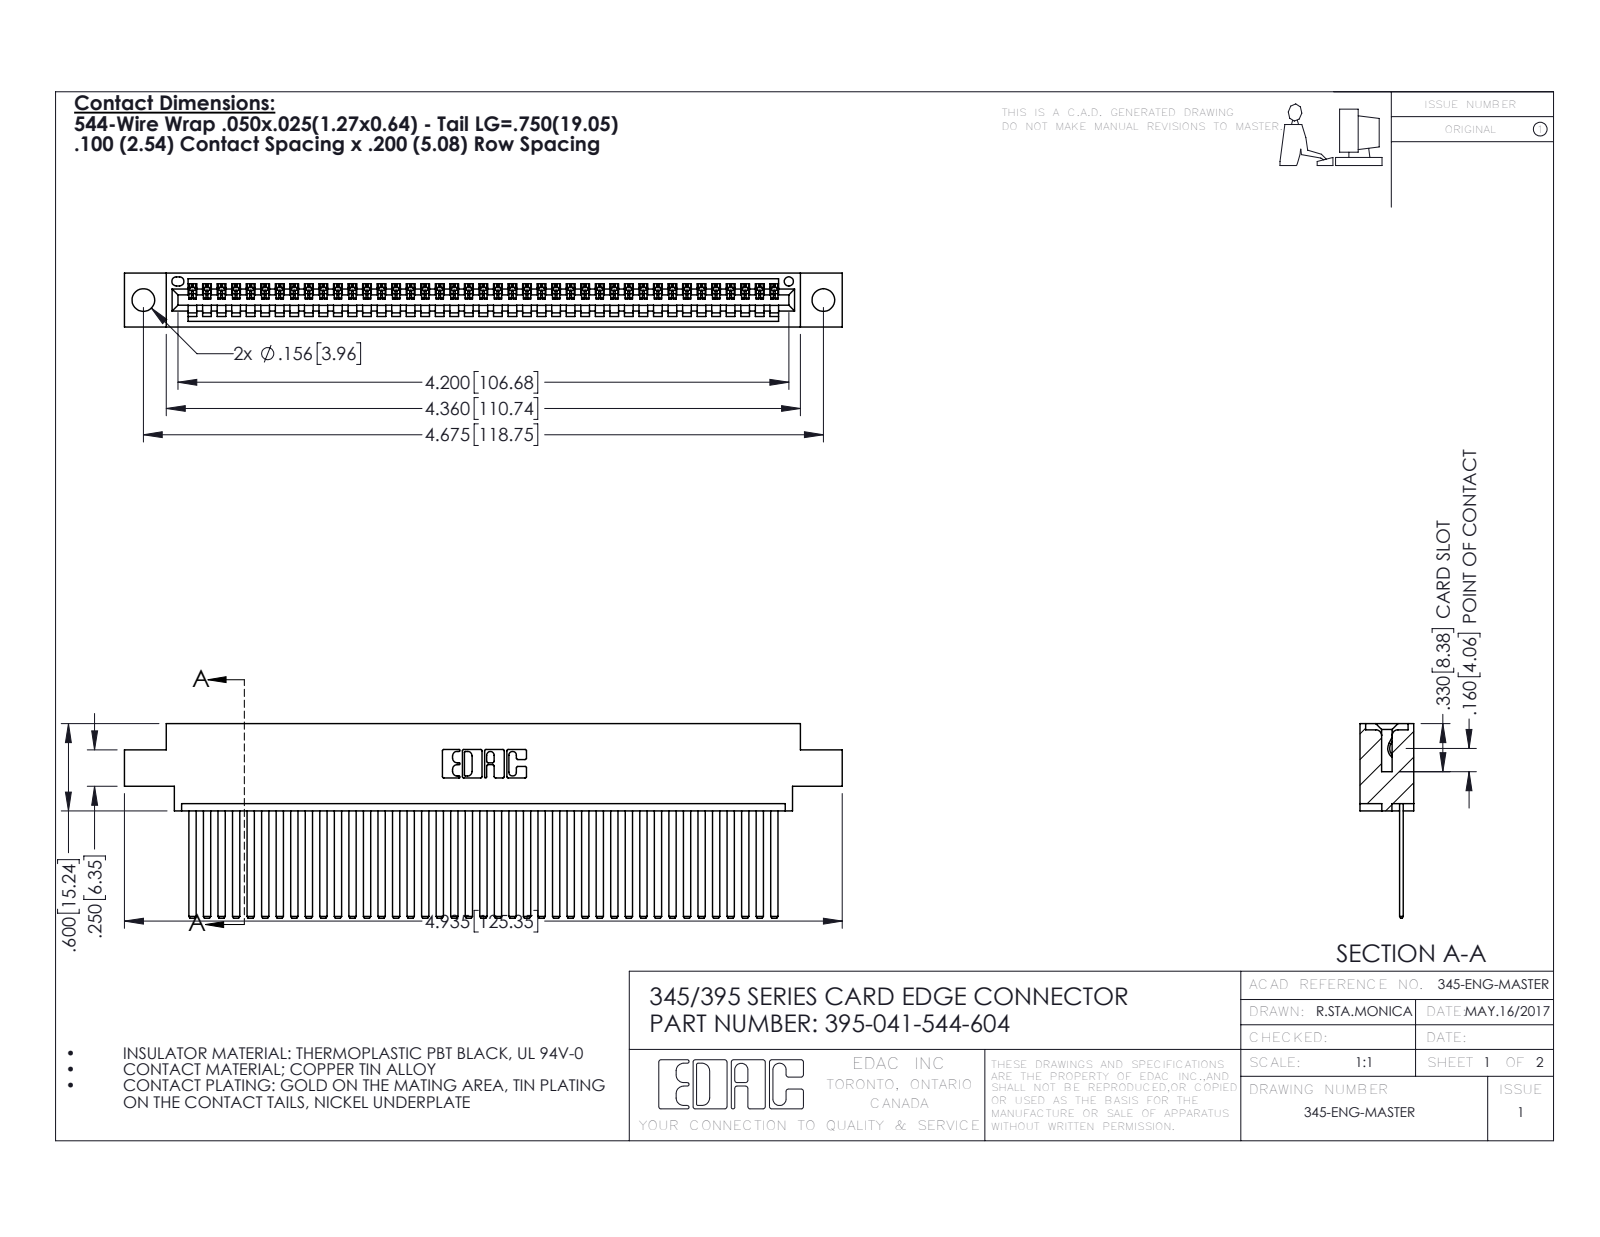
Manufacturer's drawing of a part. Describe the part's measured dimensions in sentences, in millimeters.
The part is named "395-041-544-604; 345 Part_0.170 Offset - 0.156 Dia-TH; 345-292-001_345-293-144". Its 3-D file was written by "SolidWorks 2016 (CONFIG_CONTROL_DESIGN)". It is 42 solids with 2262 faces: 1560 planar, 702 cylindrical and 0 other. Overall it measures 125.3 by 34 by 9.4 millimeters. Its volume is 12 200 cubic millimeters and its surface area 17 520 square millimeters. Round holes: 2 of diameter 4, 1 of diameter 1.6. Partial cylindrical surfaces (rounded edges, fillets, slot ends): 82 of radius 0.2, 22 of radius 0.3, 6 of radius 0.2, 6 of radius 0.8, 3 of radius 0.7, 2 of radius 0.8, 2 of radius 1, 1 of radius 0.4. The main face-to-face distances are 1.8, 7.6, 0.6, 2.5, 6.9, 9.4, 5.1, 5.7, 4.4, 3.8. The hole center spacings are 6.9, 112.8, 118.7.
